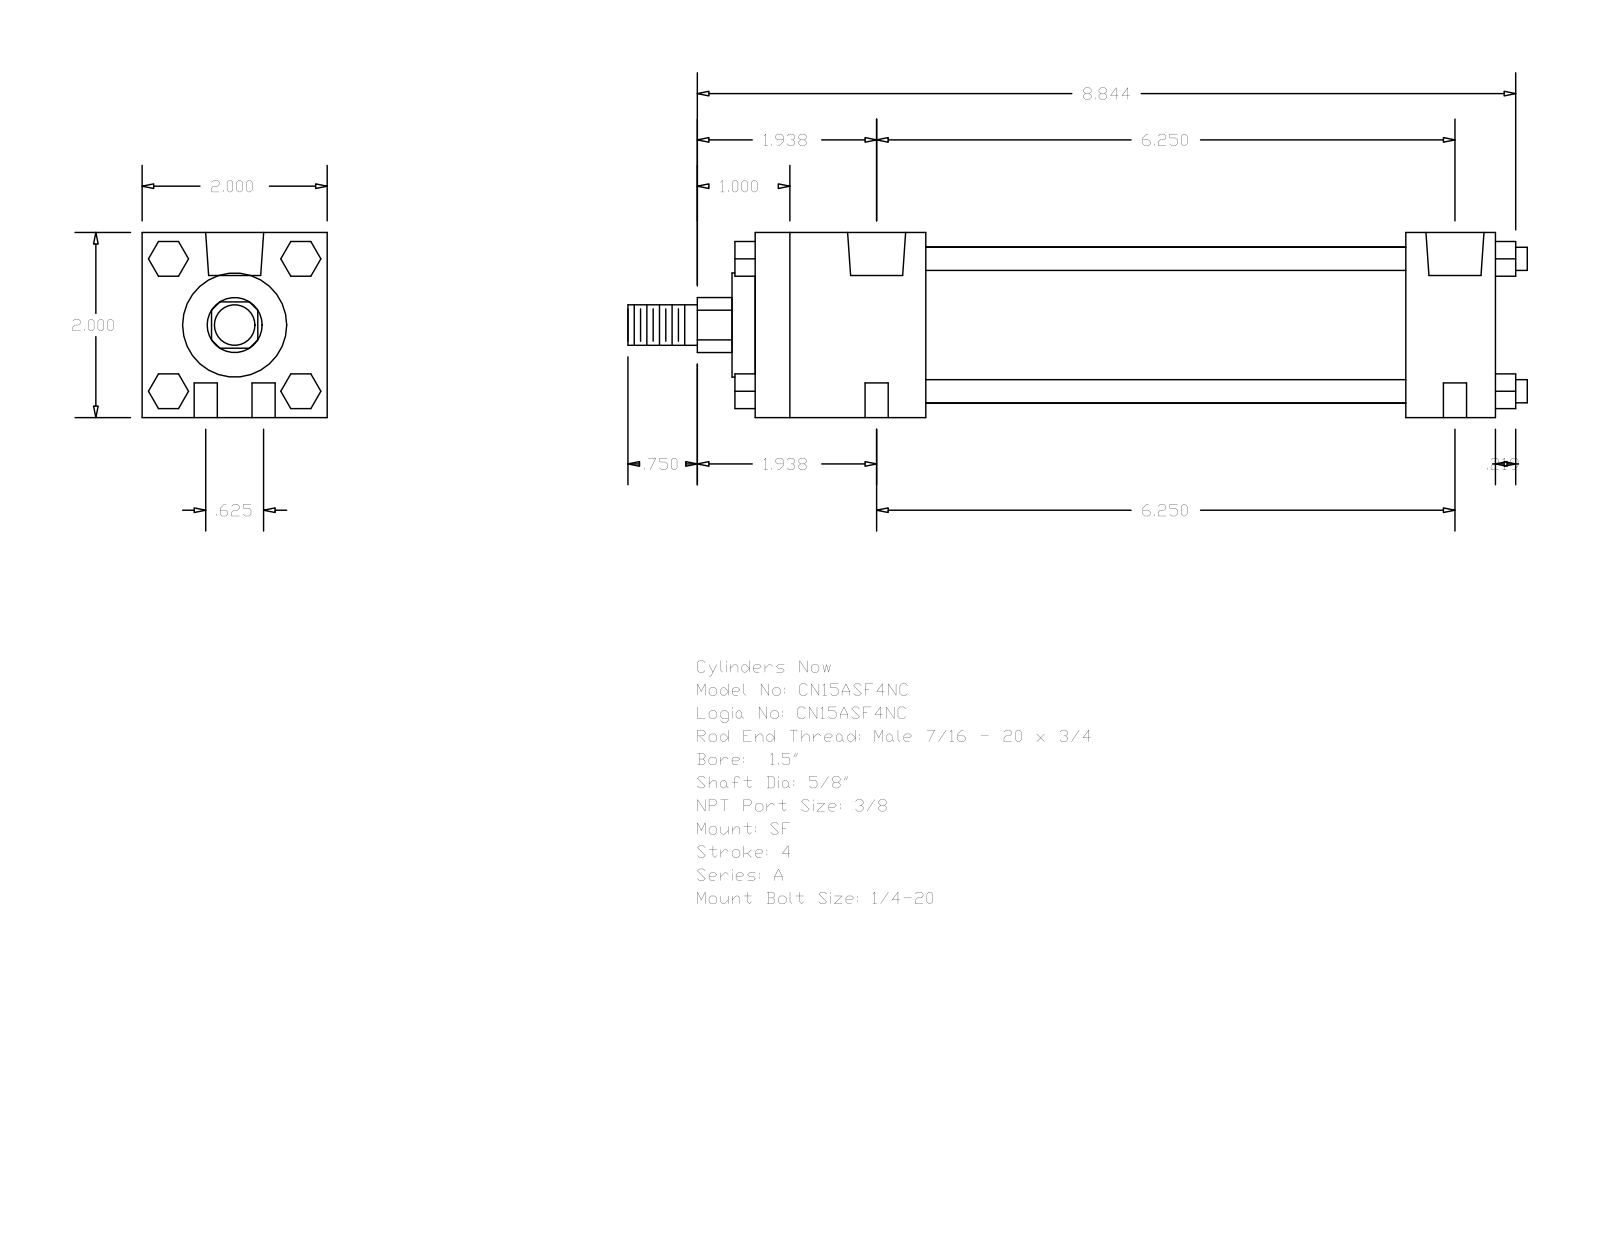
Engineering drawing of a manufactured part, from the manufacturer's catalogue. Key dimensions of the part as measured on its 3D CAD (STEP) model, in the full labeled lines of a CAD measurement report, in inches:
Part name (STEP PRODUCT): A_SF__0150_0.625
STEP written by: GSSL Pune (CONFIG_CONTROL_DESIGN)
Units: inches
Bodies: 0 solids, 124 faces (94 planar, 30 cylindrical, 0 other)
Overall size (bounding box): 9.719 × 2 × 2
Round holes (diameter × count): ⌀0.25 ×4, ⌀0.219 ×2, ⌀0.627 ×2
Round bosses / shafts (diameter × count): ⌀0.25 ×4, ⌀1.69 ×1, ⌀1.125 ×1, ⌀0.625 ×1, ⌀0.437 ×1
Partial cylindrical surfaces — rounded edges, fillets, slot ends (radius × count): R0.297 ×1
Main face-to-face distances: 2, 8, 1.844, 7.031, 5.187, 6.156, 0.969, 0.25, 0.375, 2.094
Hole centre spacings: 0.313, 6.258, 6.25, 0.625, 6.281, 5.937
